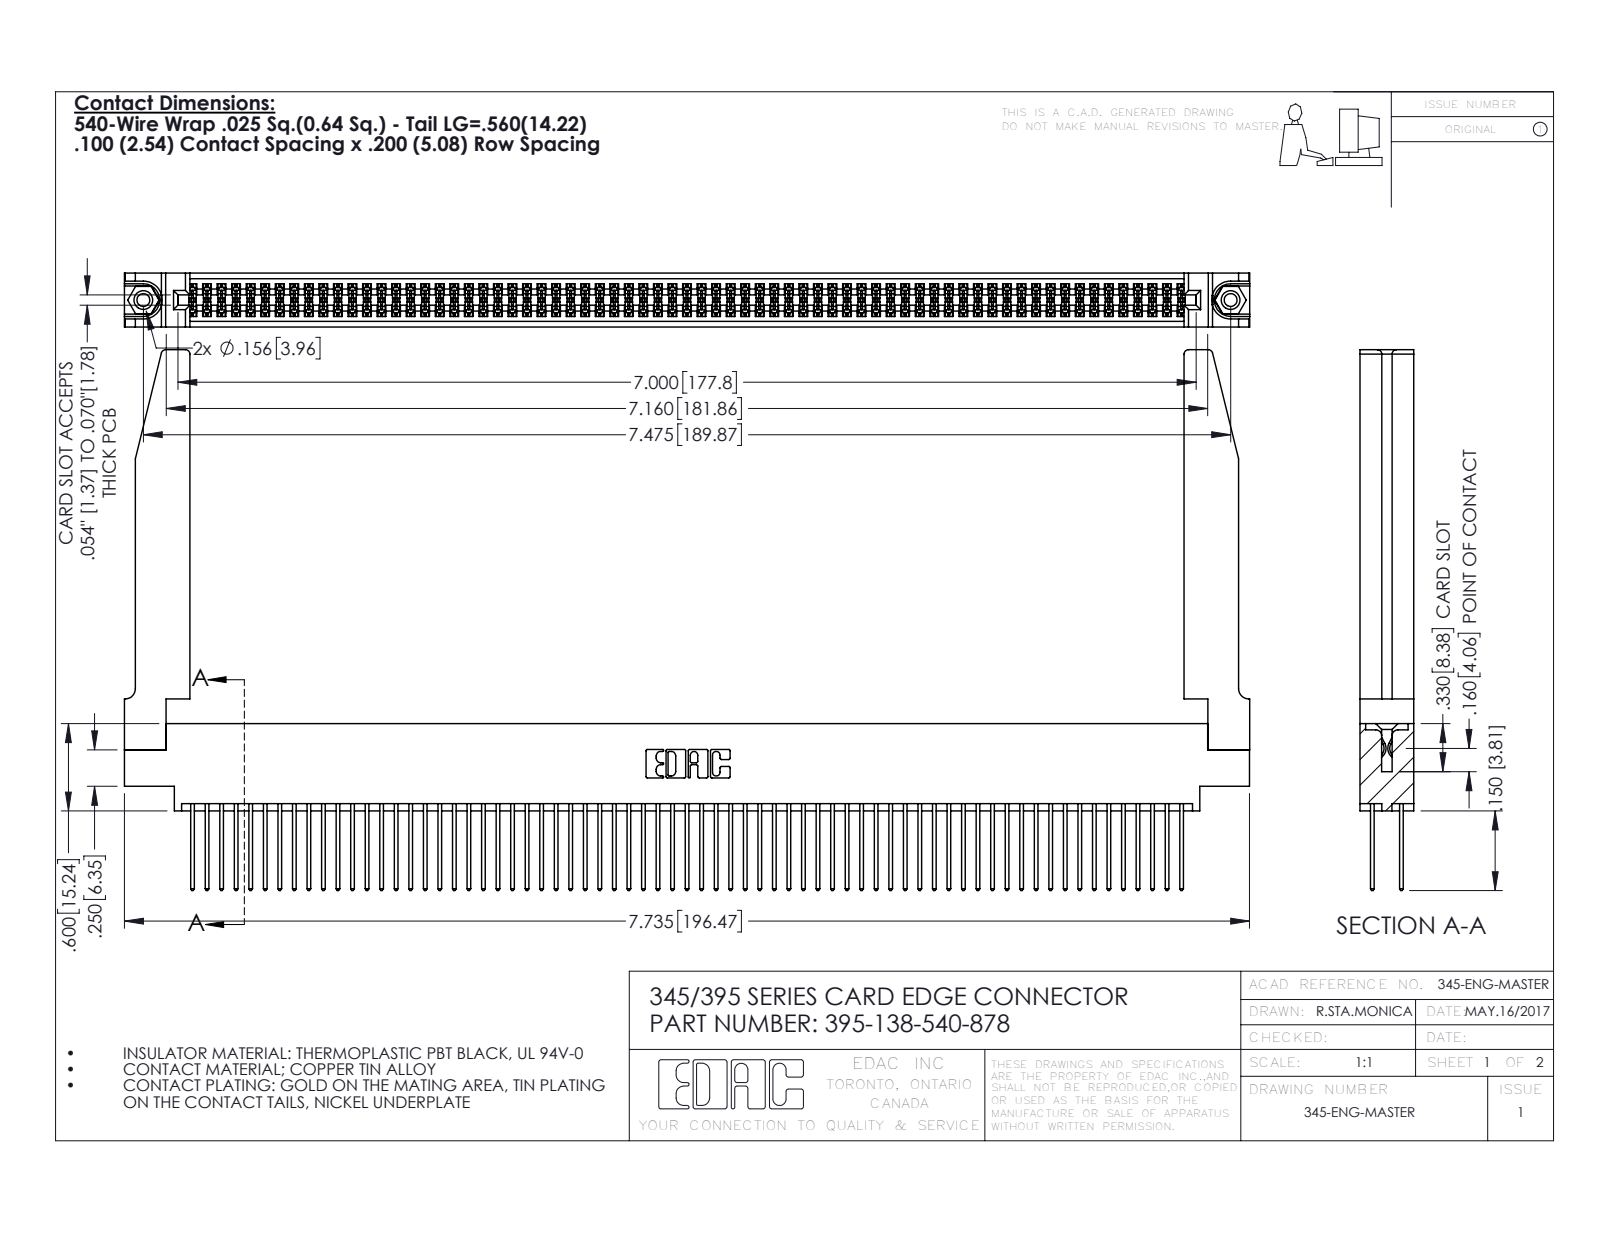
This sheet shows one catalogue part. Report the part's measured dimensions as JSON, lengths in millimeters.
{"part_name": "345 Part_0.170 Offset - 0.156 Dia-TH; 345-250-001_345-250-001-102; 395-138-540-878; 345-220-078_345-220-078 (+1 more)", "step_written_by": "SolidWorks 2016 (CONFIG_CONTROL_DESIGN)", "units": "millimeters", "bodies": {"solids": 143, "faces": 7264, "planar": 4780, "cylindrical": 2432, "other": 52}, "overall_size": [196.5, 94.4, 9.4], "volume_mm3": 27510, "surface_area_mm2": 39120, "round_holes": [[2.3, 2], [3.2, 2], [4, 2], [1.6, 1]], "round_bosses_or_shafts": [[3.9, 2]], "partial_cylinders_radius": [[0.2, 207], [0.3, 138], [0.3, 22], [0.8, 8], [0.2, 6], [0.8, 6], [0.7, 3], [0.4, 2]], "face_to_face_distances": [1.8, 7.6, 9.4, 2.5, 6.9, 0.6, 5.1, 5.7, 4.4, 3.8], "hole_center_spacings": [6.9, 183.9, 189.9]}
